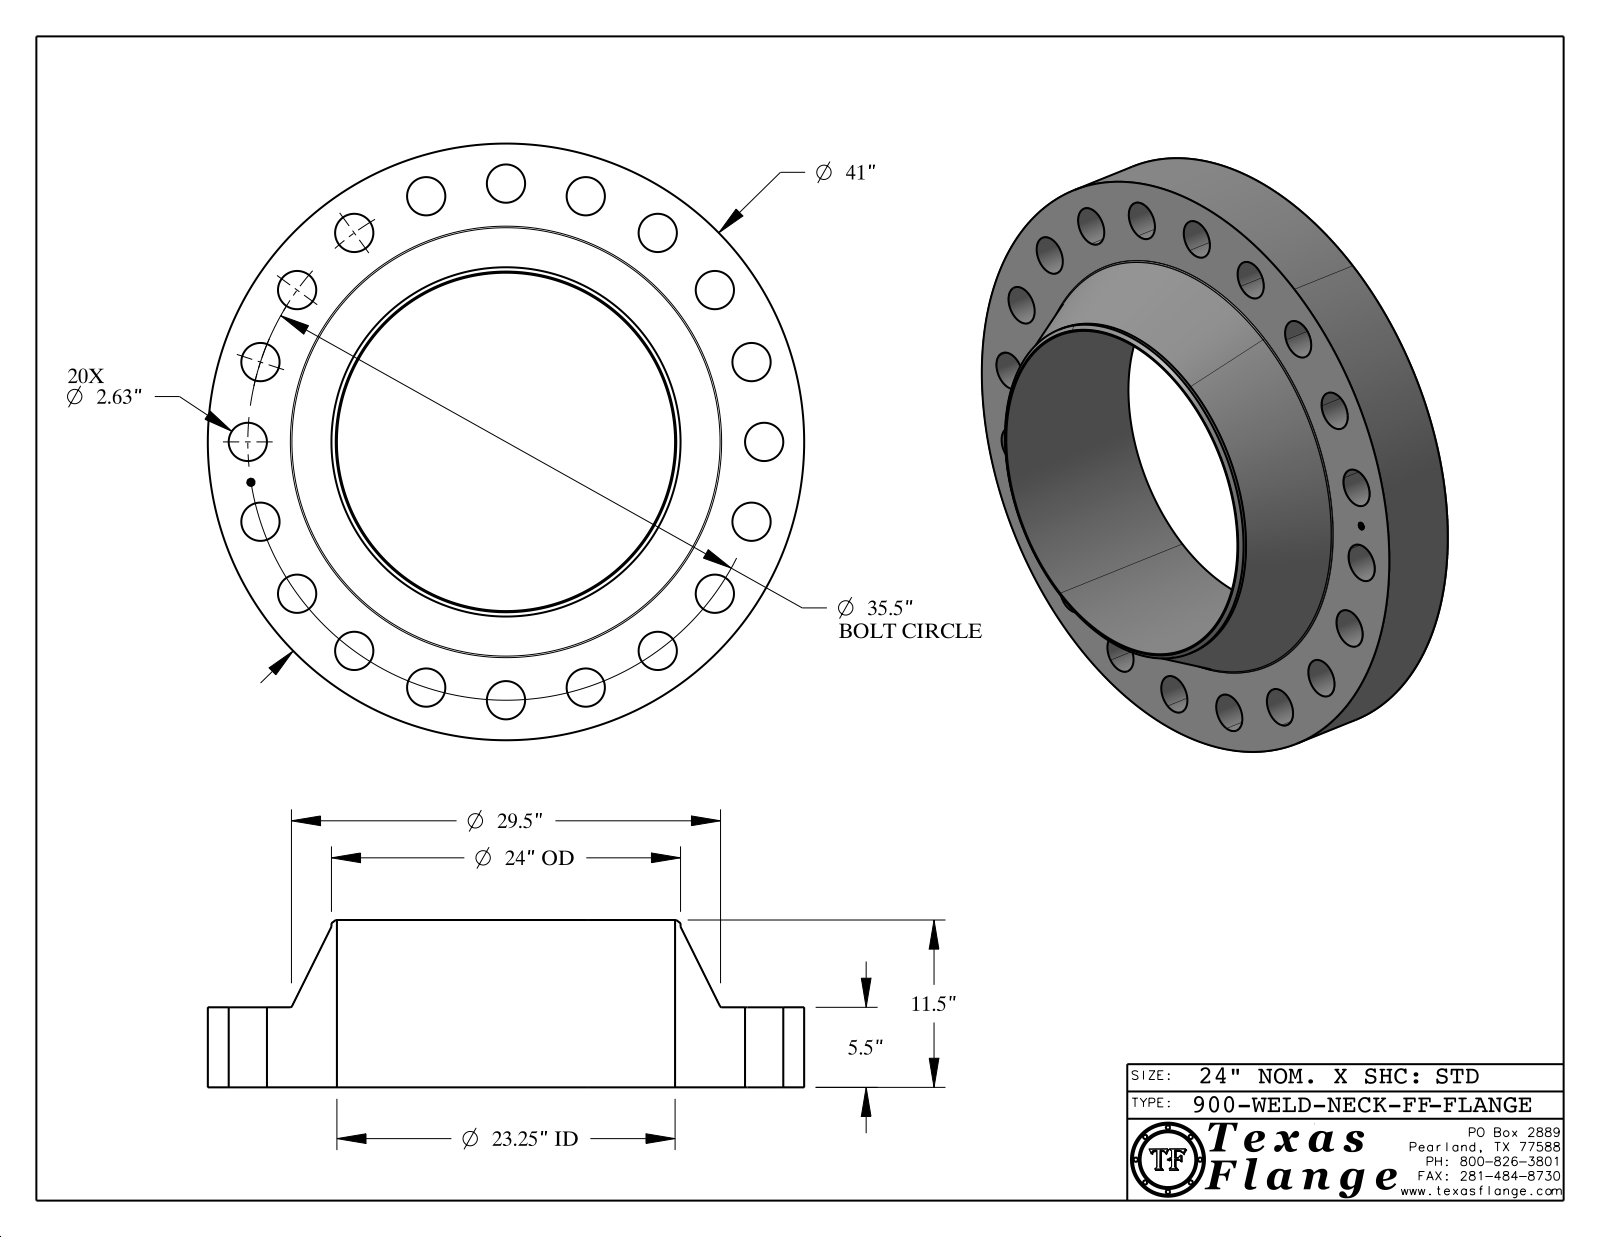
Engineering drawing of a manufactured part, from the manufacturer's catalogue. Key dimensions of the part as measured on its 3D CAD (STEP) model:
Part name (STEP PRODUCT): 900-WELD-NECK-FF
STEP written by: CATIA V5 STEP AP214 (AUTOMOTIVE_DESIGN)
Units: inches
Bodies: 1 solid, 440 faces (368 planar, 66 cylindrical, 6 other)
Overall size (bounding box): 41 × 41 × 11.5
Volume: 5 111 in³ · Surface area: 4 342 in²
Round holes (diameter × count): ⌀2.63 ×20, ⌀0.495 ×1, ⌀23.25 ×1
Round bosses / shafts (diameter × count): ⌀0.03 ×8, ⌀41 ×1, ⌀24 ×1, ⌀0.39 ×1
Main face-to-face distances: 5.5, 11.5, 6, 5.485, 0.015, 6.015, 0.148, 0.144, 0.027, 0.096
Hole centre spacings: 17.75, 10.97, 28.72, 31.631, 16.117, 20.866, 25.102, 33.762
